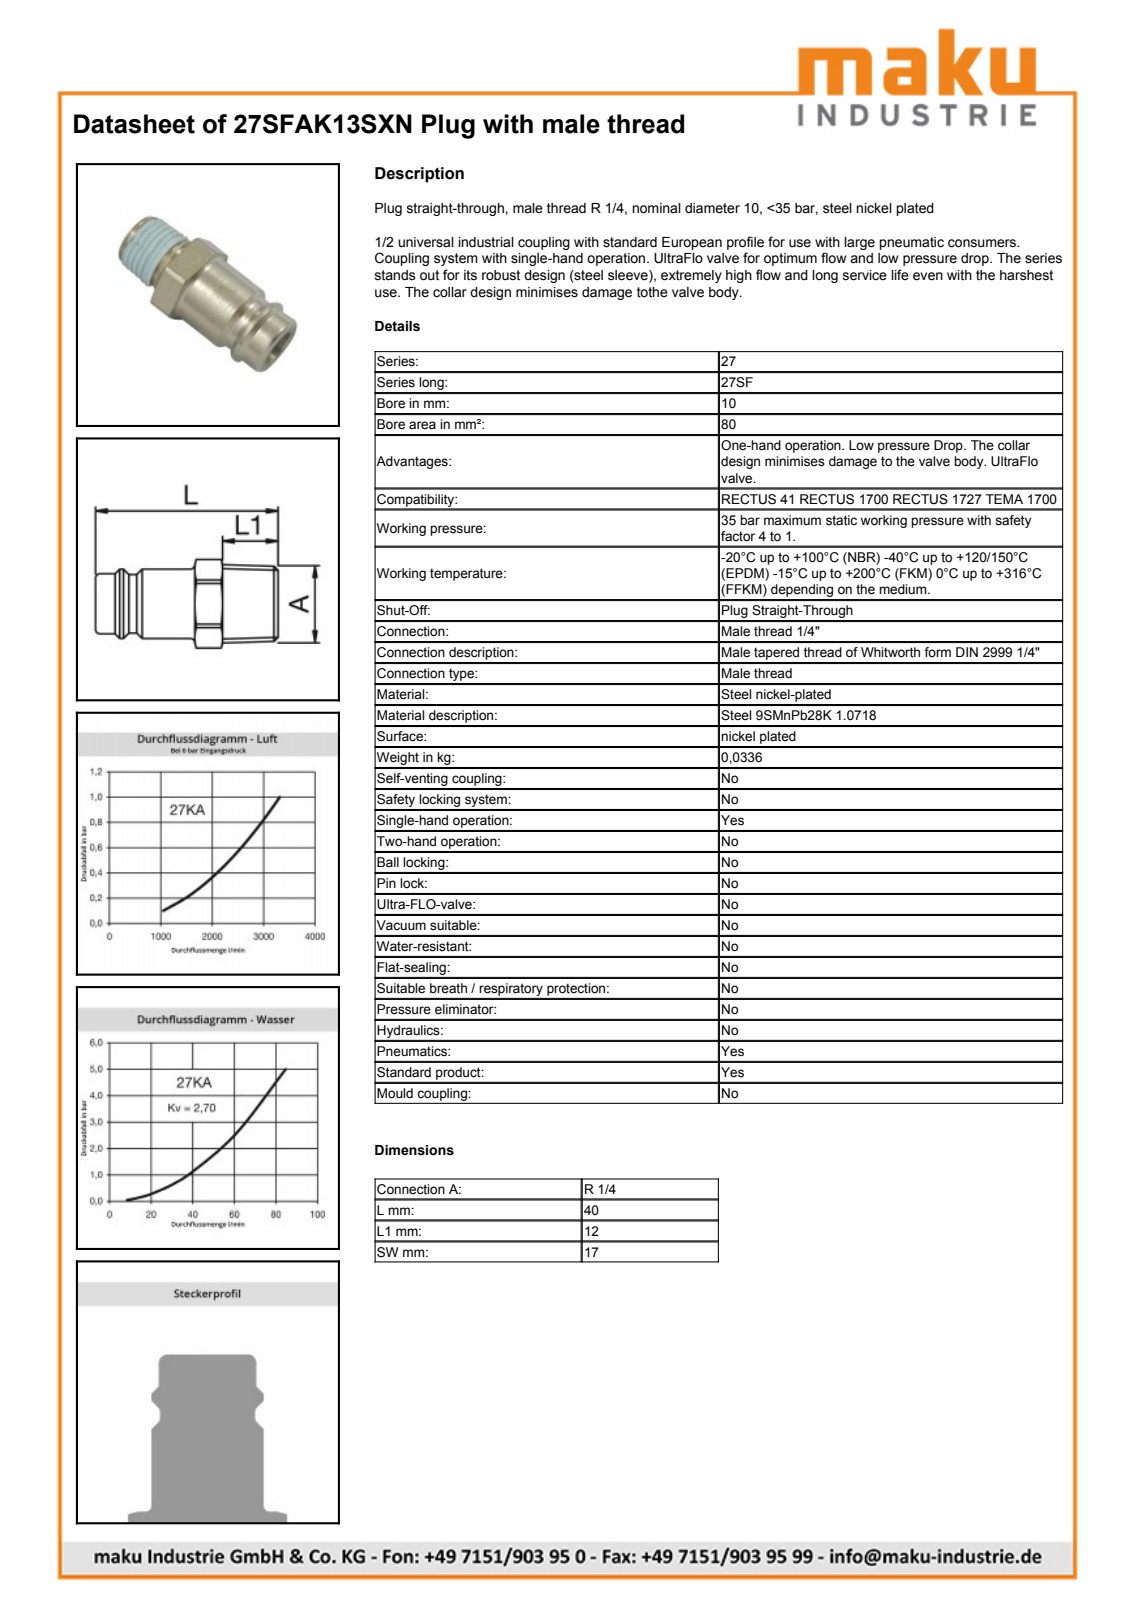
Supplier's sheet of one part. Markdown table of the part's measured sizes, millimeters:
| quantity | value |
| --- | --- |
| part name | D106709 |
| STEP written by | Autodesk Inventor 2011 (AUTOMOTIVE_DESIGN) |
| units | millimeters |
| bodies | 1 solid, 42 faces (9 planar, 11 cylindrical, 22 other) |
| overall size | 39.5 × 19.15 × 17 |
| volume | 4 556 mm³ |
| surface area | 3 112 mm² |
| round holes (diameter × count) | 8 × 1 |
| round bosses / shafts (diameter × count) | 15 × 1, 13 × 1, 12.65 × 1 |
| partial cylindrical surfaces (radius × count) | 9.57 × 1 |
| main face-to-face distances | 17, 27.5, 39.5, 12 |
